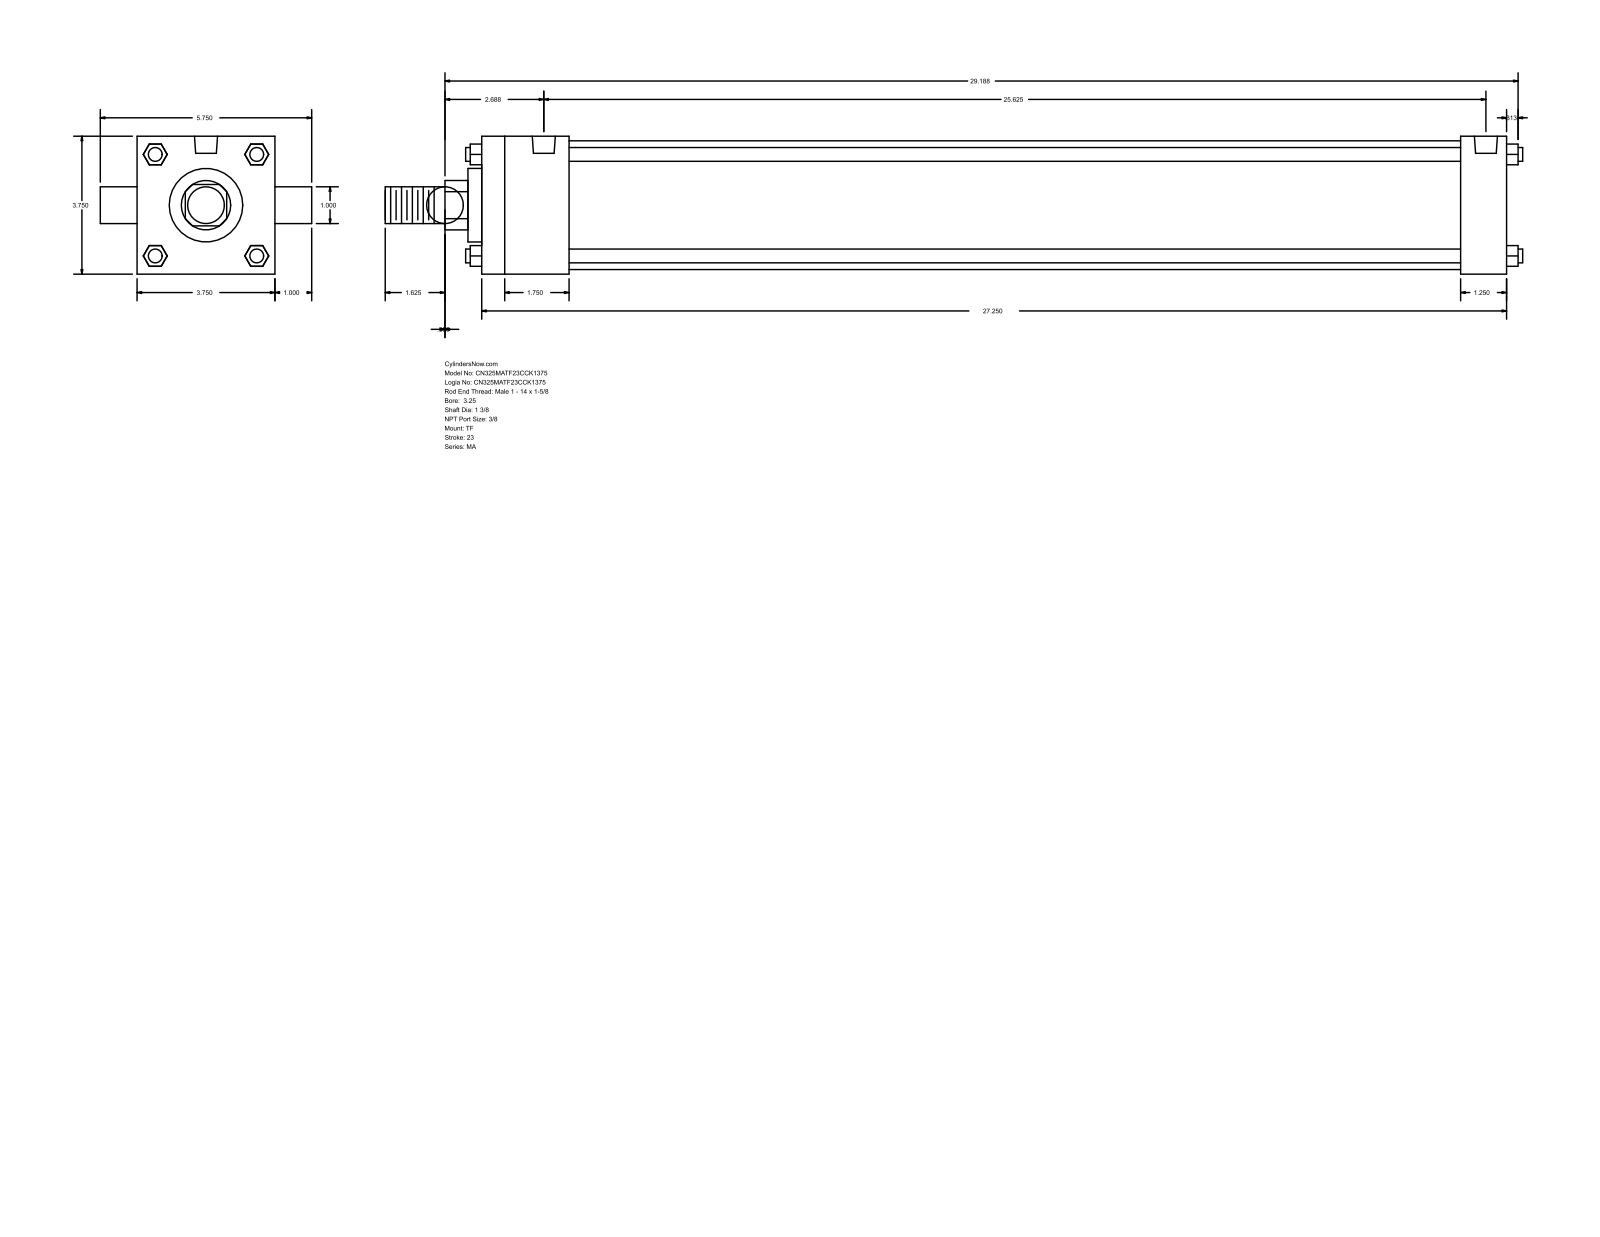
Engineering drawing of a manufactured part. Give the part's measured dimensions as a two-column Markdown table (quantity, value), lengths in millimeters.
| quantity | value |
| --- | --- |
| part name | MA_TF__0325_1.375 |
| STEP written by | GSSL Pune (CONFIG_CONTROL_DESIGN) |
| units | millimeters |
| bodies | 0 solids, 120 faces (92 planar, 28 cylindrical, 0 other) |
| overall size | 785.81 × 146.05 × 95.25 |
| round holes (diameter × count) | 11.11 × 3, 15.93 × 2 |
| round bosses / shafts (diameter × count) | 9.53 × 4, 25.4 × 2, 88.9 × 1, 50.8 × 1, 34.92 × 1 |
| partial cylindrical surfaces (radius × count) | 17.06 × 1 |
| main face-to-face distances | 95.24, 708.02, 60.32, 676.27, 615.95, 647.7, 31.75, 9.52, 69.84, 685.79 |
| hole center spacings | 4.76, 4.77, 641.35, 646.11, 646.12, 650.88 |
